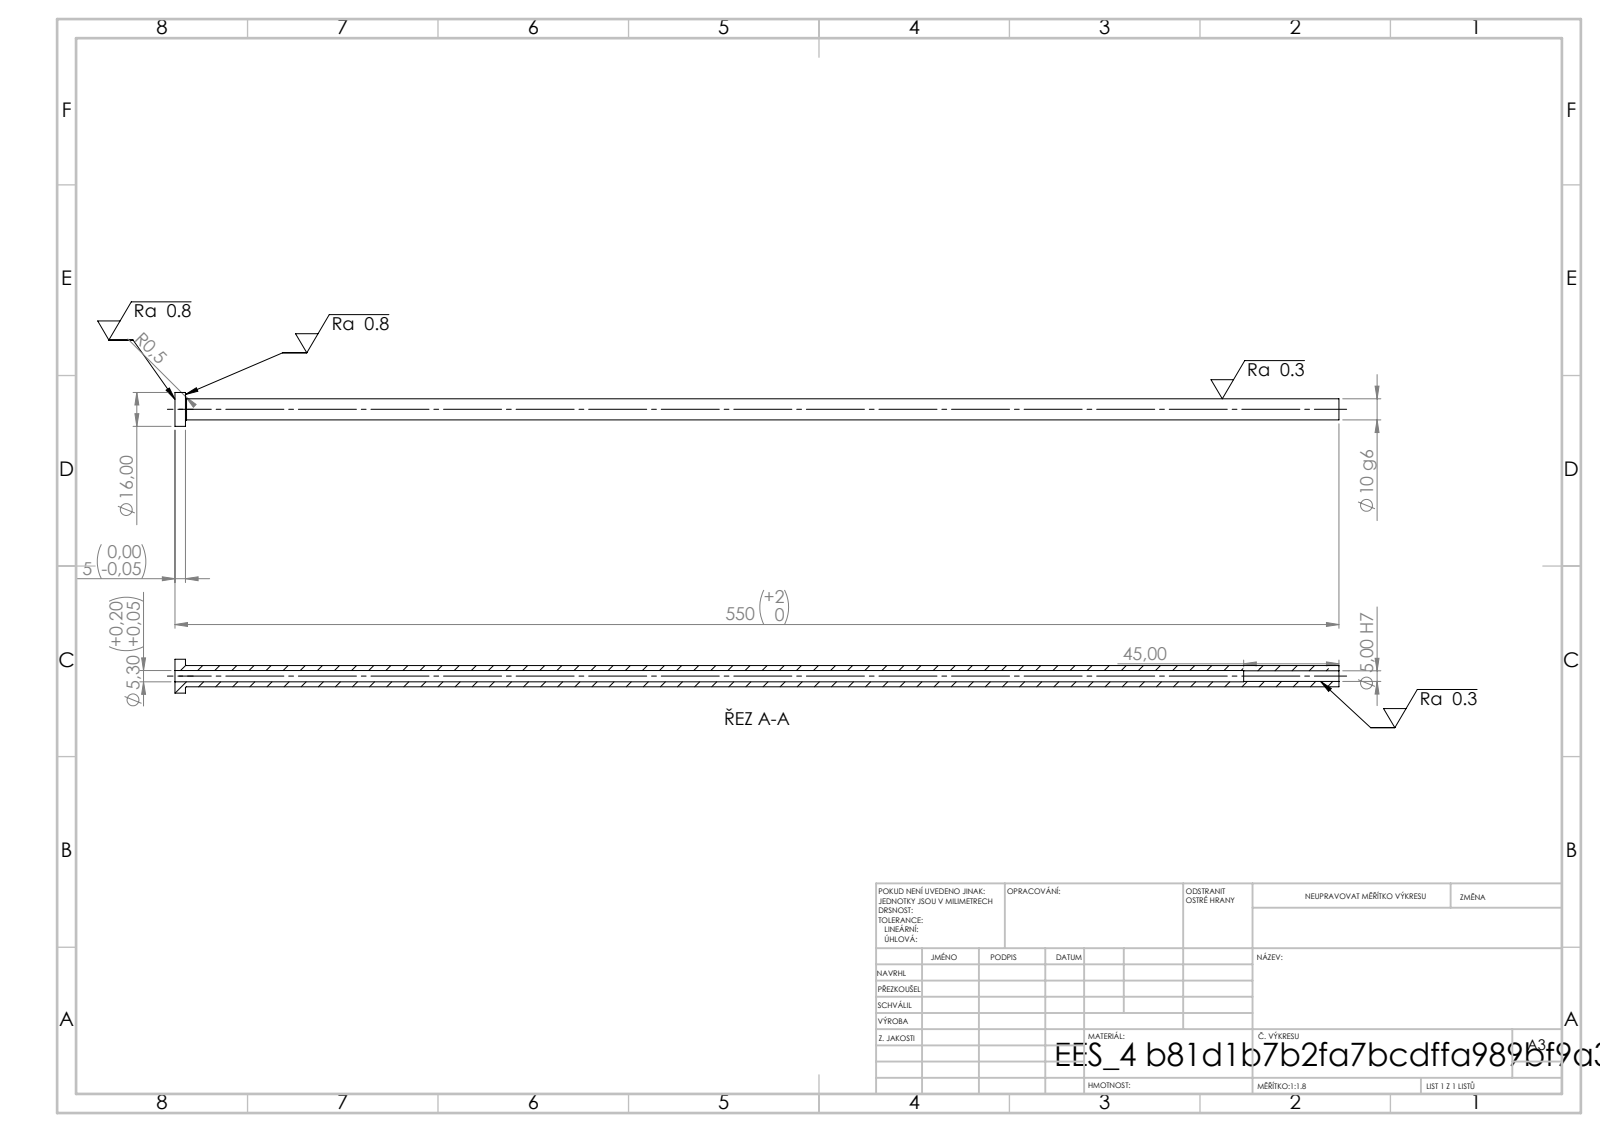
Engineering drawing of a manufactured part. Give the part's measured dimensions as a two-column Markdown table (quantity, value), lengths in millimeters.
| quantity | value |
| --- | --- |
| STEP written by | SolidWorks 2019 (CONFIG_CONTROL_DESIGN) |
| units | millimeters |
| bodies | 1 solid, 14 faces (4 planar, 8 cylindrical, 2 other) |
| overall size | 550 × 16 × 16 |
| volume | 31 786 mm³ |
| surface area | 26 845 mm² |
| round holes (diameter × count) | 5 × 1, 5.3 × 1 |
| round bosses / shafts (diameter × count) | 16 × 1, 10 × 1 |
| main face-to-face distances | 5, 550, 545, 505, 500, 45 |
